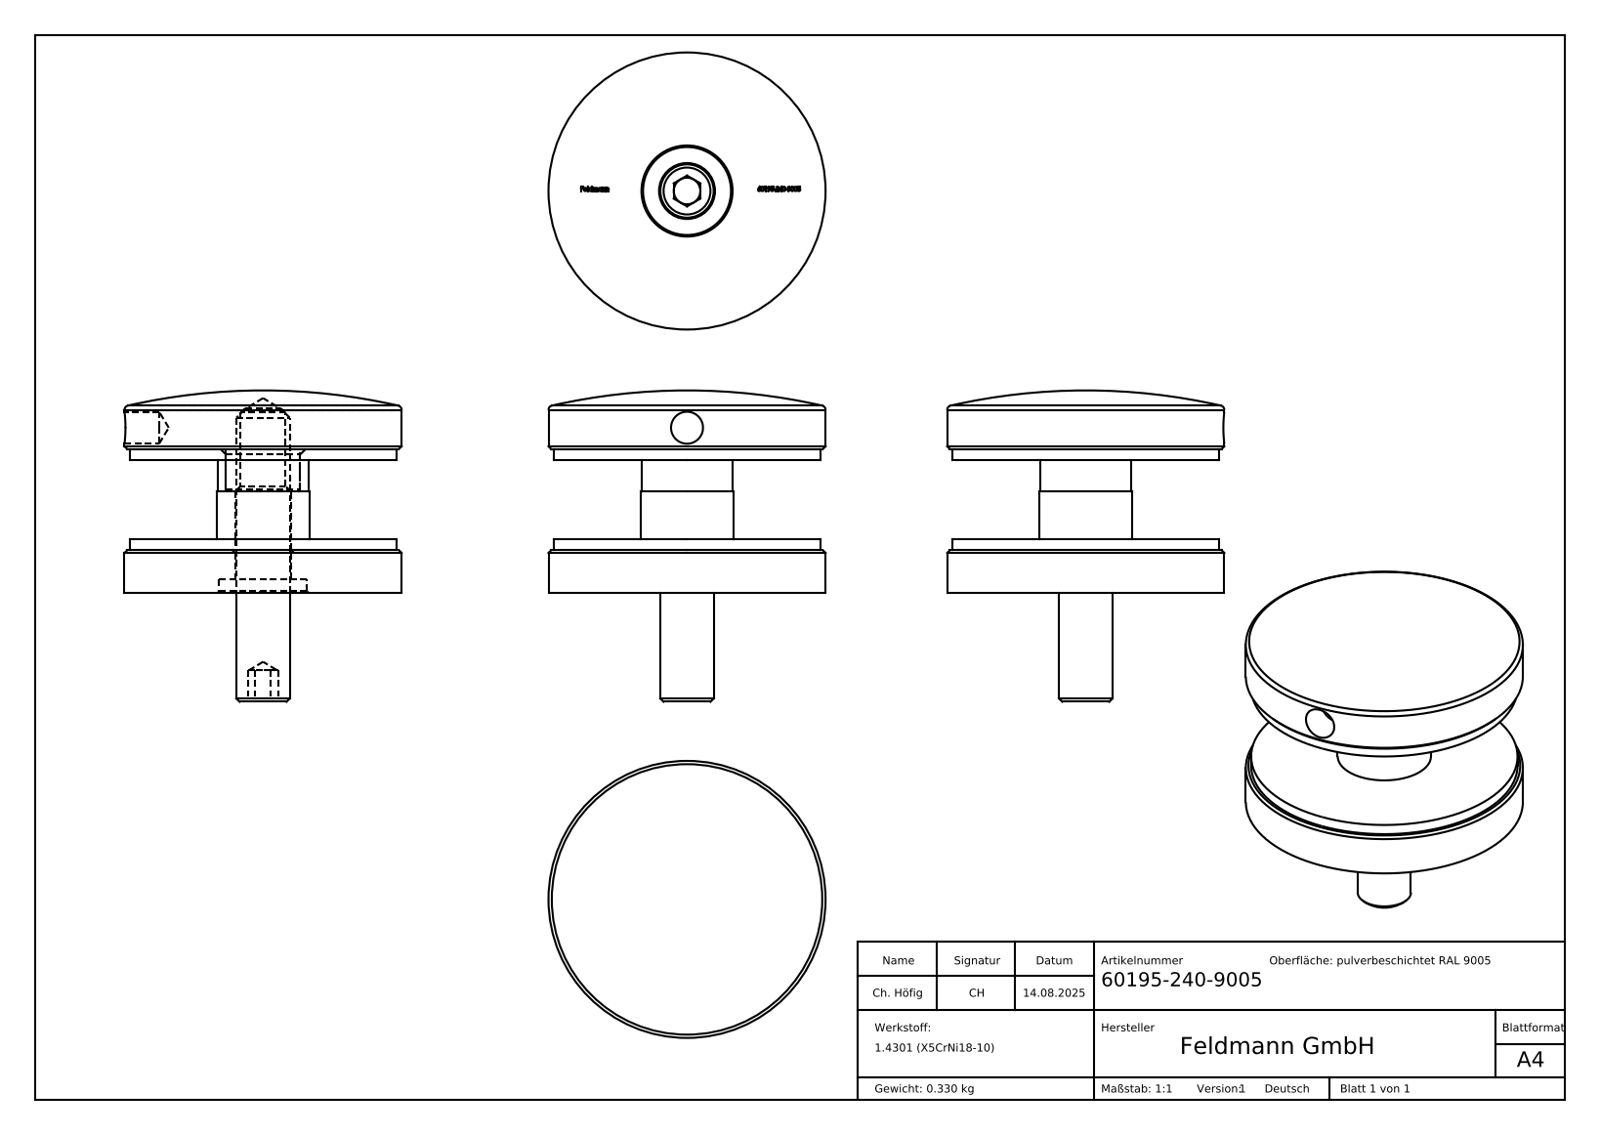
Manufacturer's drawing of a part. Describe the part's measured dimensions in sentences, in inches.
The part is named "6019X-240 Konfig Teil1_6019X-240 Teil1; 6019X-240 Konfig Teil5_60195-240 Teil5; 60195-240-9005; 6019X-240 Konfig Teil2_60195-240-9005 Teil2 (+3 more)". Its 3-D file was written by "SolidWorks 2018 (CONFIG_CONTROL_DESIGN)". It is 6 solids with 329 faces: 167 planar, 15 cylindrical and 147 other. Overall it measures 2.301 by 2.047 by 2.047 inches. Its volume is 3.022 cubic inches and its surface area 36.82 square inches. Round holes: 1 of diameter 0.236, 1 of diameter 0.335, 1 of diameter 0.413, 1 of diameter 0.551, 1 of diameter 0.65. Round bosses or shafts: 1 of diameter 2.047, 1 of diameter 1.969, 1 of diameter 0.689, 1 of diameter 0.669, 1 of diameter 0.394. The main face-to-face distances are 0.748, 0.079, 0.669, 0.315, 0.394, 1.063, 0.984, 0.591, 0.236, 0.433.
